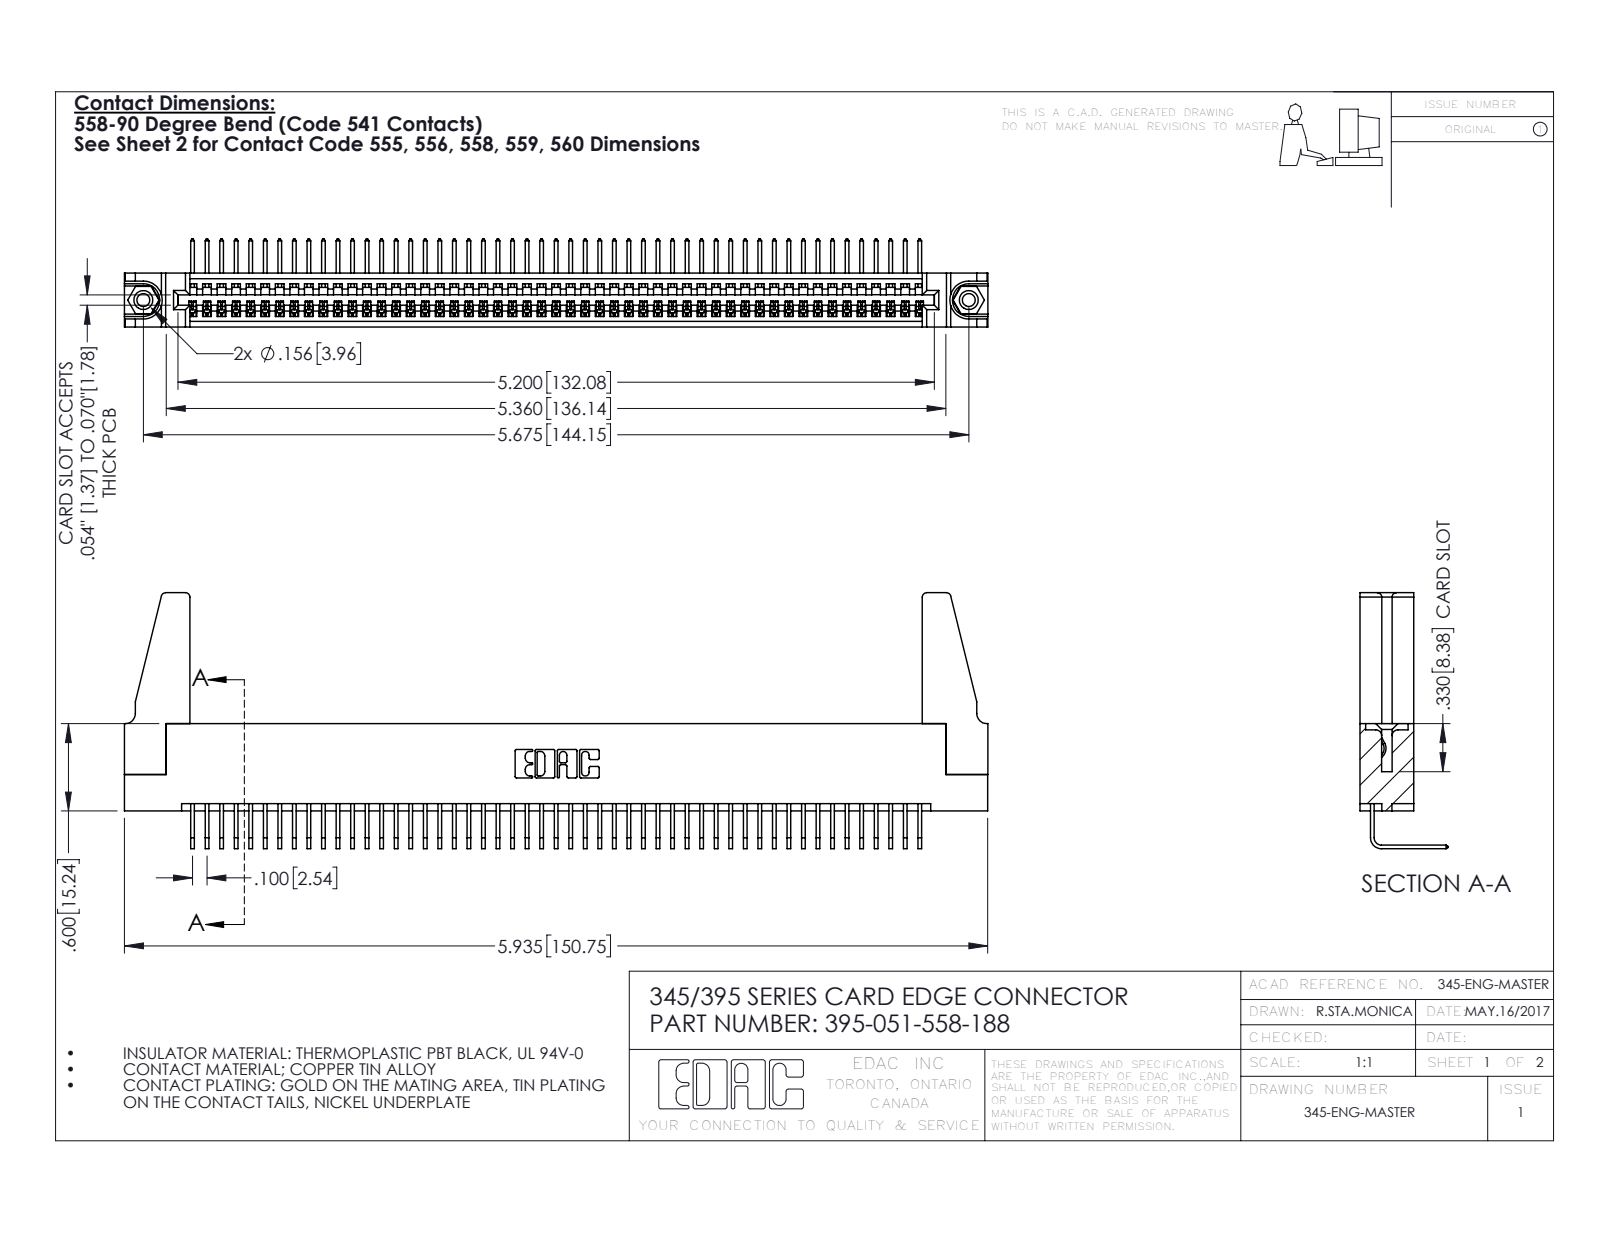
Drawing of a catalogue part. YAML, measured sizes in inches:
part_name: "345-292-001_558 Tail - 2; 395-051-558-188; 345-220-078_345-220-088; 345 Part_Flush Mounting Lugs - 0.156 Dia-TH (+1 more)"
step_written_by: "SolidWorks 2016 (CONFIG_CONTROL_DESIGN)"
units: inches
bodies: {solids: 56, faces: 3310, planar: 2294, cylindrical: 1000, other: 16}
overall_size: [5.936, 1.759, 0.605]
volume: 1.087
surface_area: 36.59
round_holes:
  - {diameter: 0.089, count: 2}
  - {diameter: 0.125, count: 2}
  - {diameter: 0.156, count: 2}
  - {diameter: 0.064, count: 1}
round_bosses_or_shafts:
  - {diameter: 0.155, count: 2}
partial_cylinders:
  - {radius: 0.006, count: 102}
  - {radius: 0.01, count: 22}
  - {radius: 0.03, count: 8}
  - {radius: 0.007, count: 6}
  - {radius: 0.031, count: 6}
  - {radius: 0.026, count: 3}
  - {radius: 0.031, count: 2}
  - {radius: 0.04, count: 2}
face_to_face_distances: [0.072, 0.298, 0.37, 0.2, 0.098, 0.272, 0.025, 0.225, 0.149, 0.072]
hole_center_spacings: [0.27, 5.439, 5.675]
